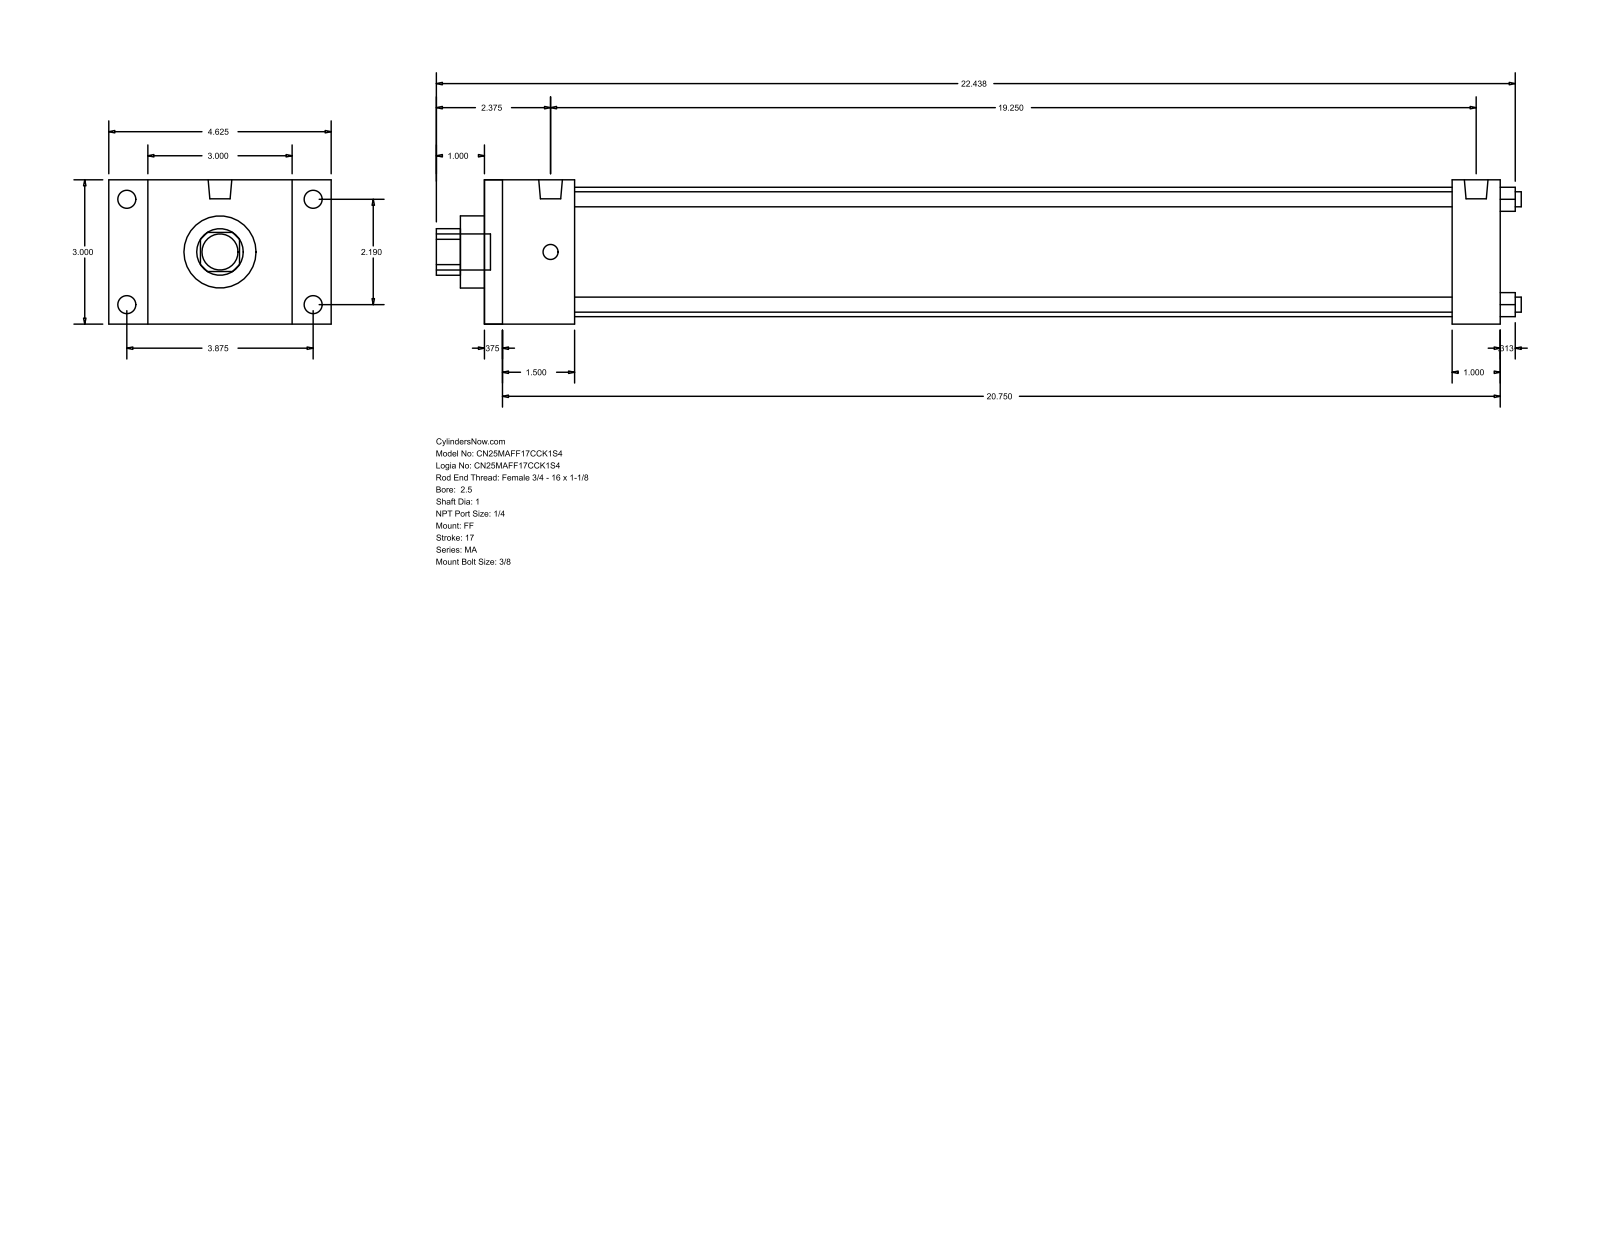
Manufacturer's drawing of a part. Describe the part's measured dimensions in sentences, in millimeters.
The part is named "MA_FF__0250_1". Its 3-D file was written by "GSSL Pune (CONFIG_CONTROL_DESIGN)". It is 0 solids with 92 faces: 64 planar, 28 cylindrical and 0 other. Overall it measures 573.09 by 117.47 by 76.2 millimeters. Round holes: 4 of diameter 7.94, 1 of diameter 25.4, 1 of diameter 38.1, 1 of diameter 68.33. Round bosses or shafts: 4 of diameter 9.53, 4 of diameter 7.94, 2 of diameter 12.49, 1 of diameter 19.05. Partial cylindrical surfaces (rounded edges, fillets, slot ends): 1 of radius 12.29. The main face-to-face distances are 76.2, 536.58, 9.52, 527.06, 25.4, 47.63, 511.18, 38.11, 501.66, 463.55. The hole center spacings are 39.33, 55.62, 78.66.
